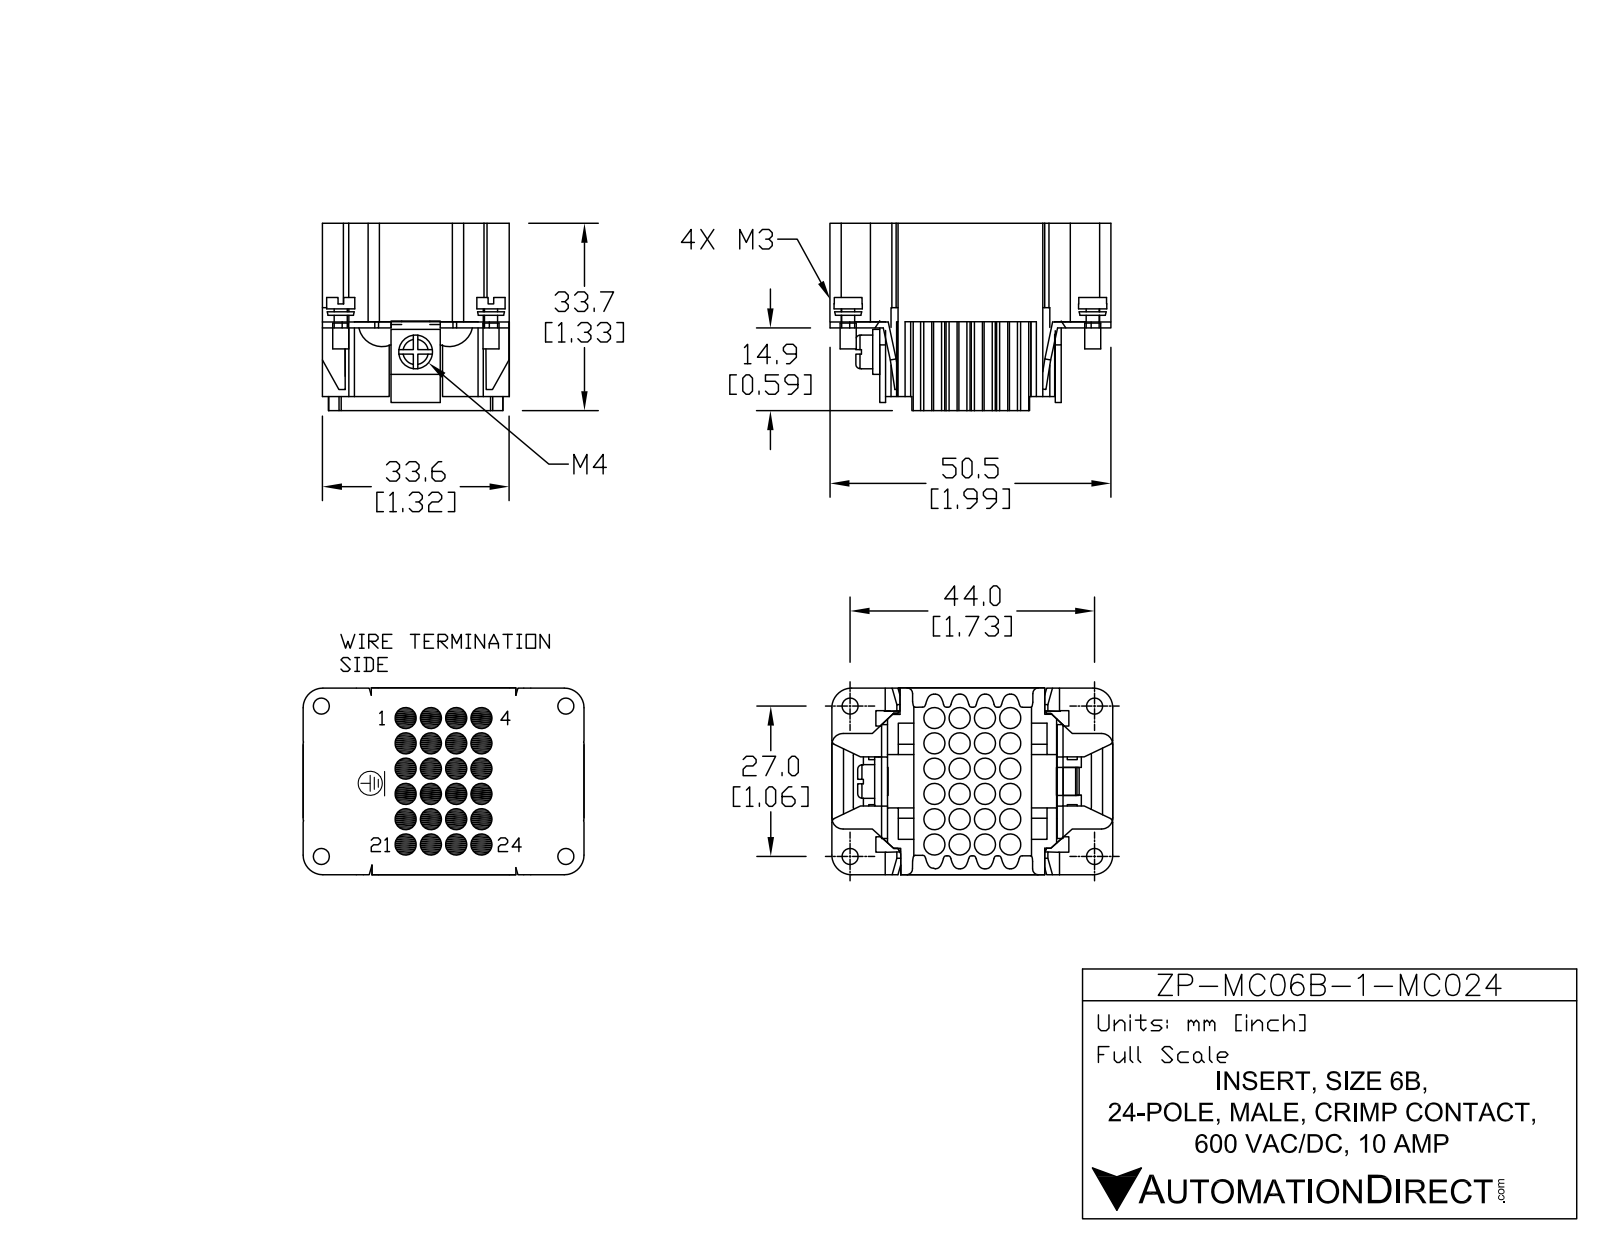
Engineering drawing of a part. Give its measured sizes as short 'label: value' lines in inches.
name: ZP-MC06B-1-MC024
written by: SolidWorks 2017 (AUTOMOTIVE_DESIGN)
unit: in
bodies: 7 solids, 541 faces (346 planar, 120 cylindrical, 75 other)
size: 1.969 × 1.378 × 1.309
volume: 0.948 in³; area: 31.41 in²
holes: 24× ⌀0.148, 4× ⌀0.098, 1× ⌀0.13
bosses: 4× ⌀0.198, 4× ⌀0.112, 4× ⌀0.091, 1× ⌀0.236
rounds: 8× R0.039, 4× R0.03, 4× R0.035, 4× R0.138, 2× R0.226
face distances: 0.041, 0.669, 0.076, 1.309, 0.08, 0.591, 0.079, 0.569, 0.122, 0.043
hole spacings: 0.396, 0.177, 0.25, 0.354, 0.56, 0.639, 0.531, 0.501
